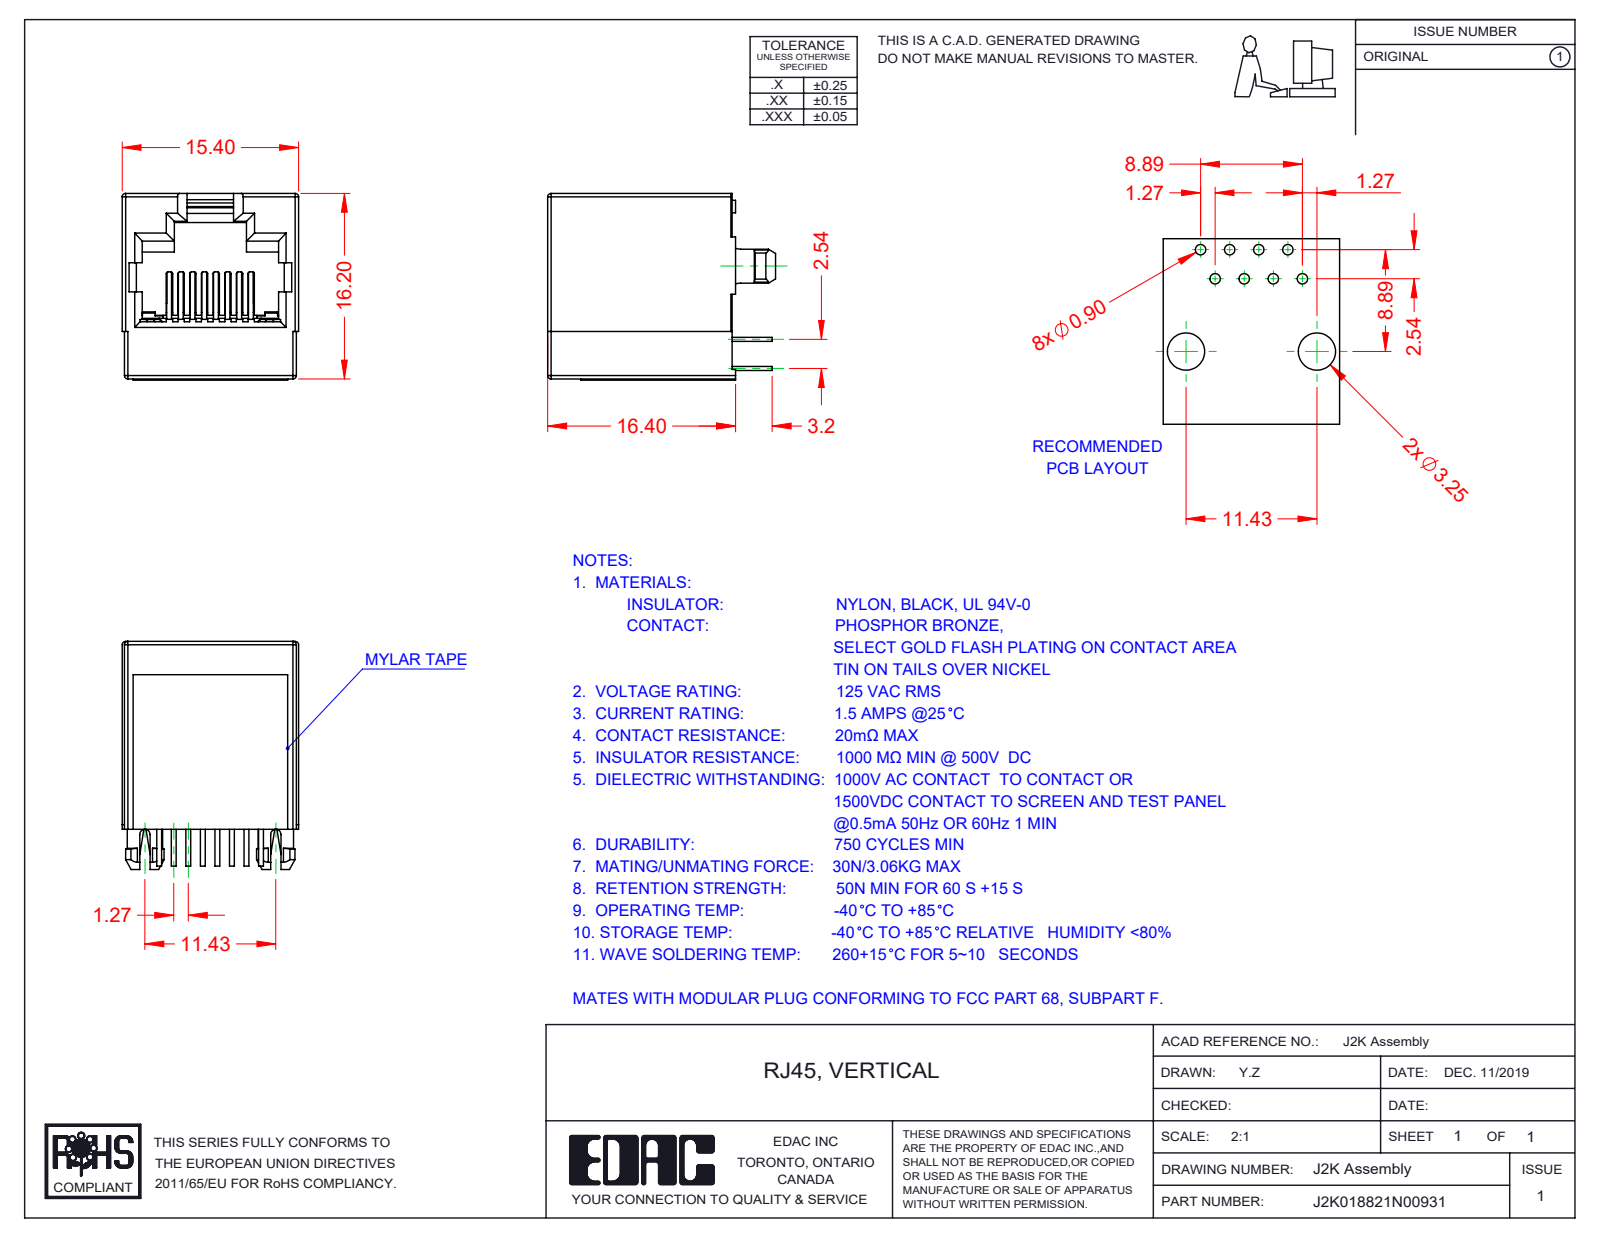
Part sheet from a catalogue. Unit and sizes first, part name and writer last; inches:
Units: inches
Overall size (bounding box): 0.783 × 0.642 × 0.606
Round bosses / shafts (diameter × count): ⌀0.122 ×2, ⌀0.043 ×2
Partial cylindrical surfaces — rounded edges, fillets, slot ends (radius × count): R0.006 ×16, R0.012 ×10, R0.02 ×3, R0.004 ×2, R0.008 ×2, R0.018 ×2, R0.024 ×2, R0.037 ×2
Main face-to-face distances: 0.638, 0.606, 0.642, 0.551, 0.055, 0.047, 0.543, 0.598, 0.02, 0.051
Volume: 0.152 in³ · Surface area: 6.715 in²
Bodies: 11 solids, 729 faces (592 planar, 113 cylindrical, 24 other)
Part name (STEP PRODUCT): 2K Mylar Tape; RJ2K018821N00931; 2K Contact Lock; 2K Insulator (+1 more)
STEP written by: SolidWorks 2016 (CONFIG_CONTROL_DESIGN)
